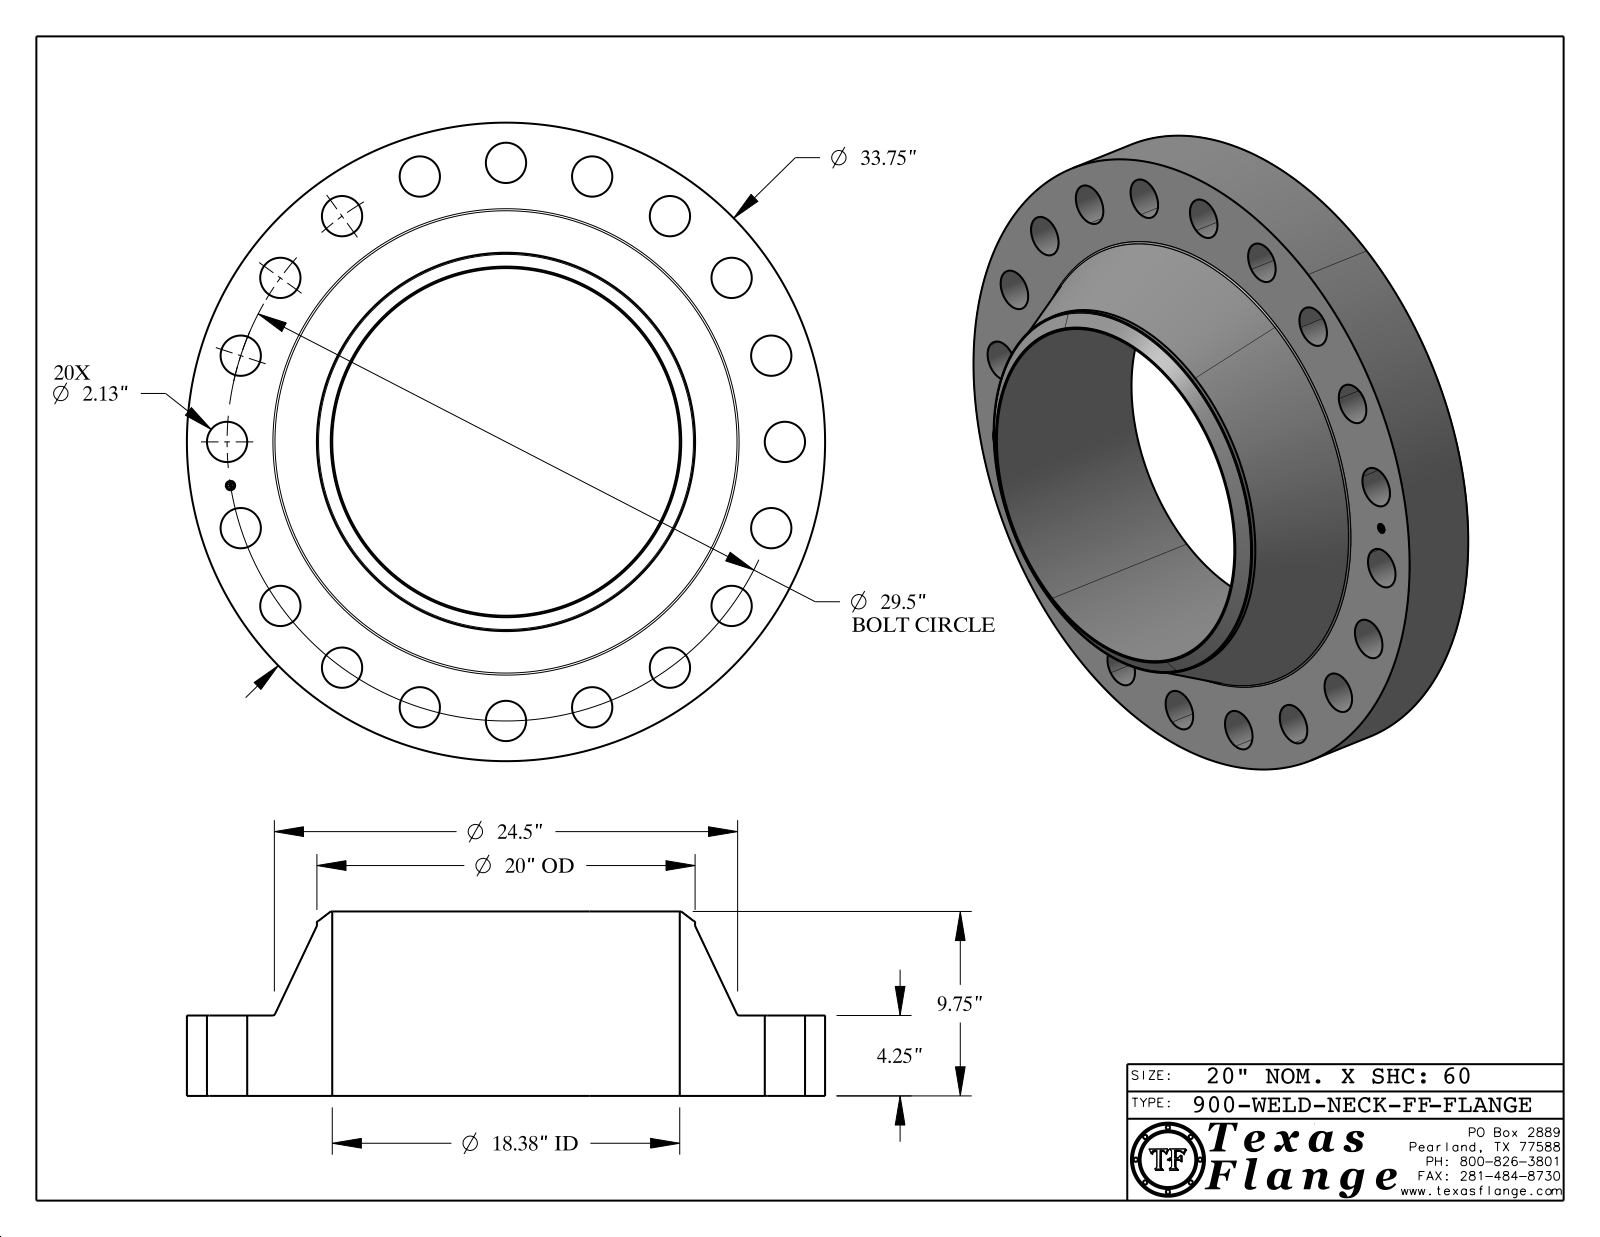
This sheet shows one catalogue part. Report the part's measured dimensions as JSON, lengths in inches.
{"part_name": "900-WELD-NECK-FF", "step_written_by": "CATIA V5 STEP AP214 (AUTOMOTIVE_DESIGN)", "units": "inches", "bodies": {"solids": 1, "faces": 444, "planar": 368, "cylindrical": 66, "other": 10}, "overall_size": [33.75, 33.75, 9.75], "volume_in3": 2989, "surface_area_in2": 2932, "round_holes": [[2.13, 20], [0.495, 1], [18.376, 1]], "round_bosses_or_shafts": [[0.03, 8], [33.75, 1], [20, 1], [0.39, 1]], "face_to_face_distances": [4.25, 9.75, 5.5, 4.235, 0.015, 5.515, 0.148, 0.145, 0.027, 0.096], "hole_center_spacings": [14.75, 29.137, 4.615, 17.34, 20.859, 23.866, 26.285, 9.116]}
